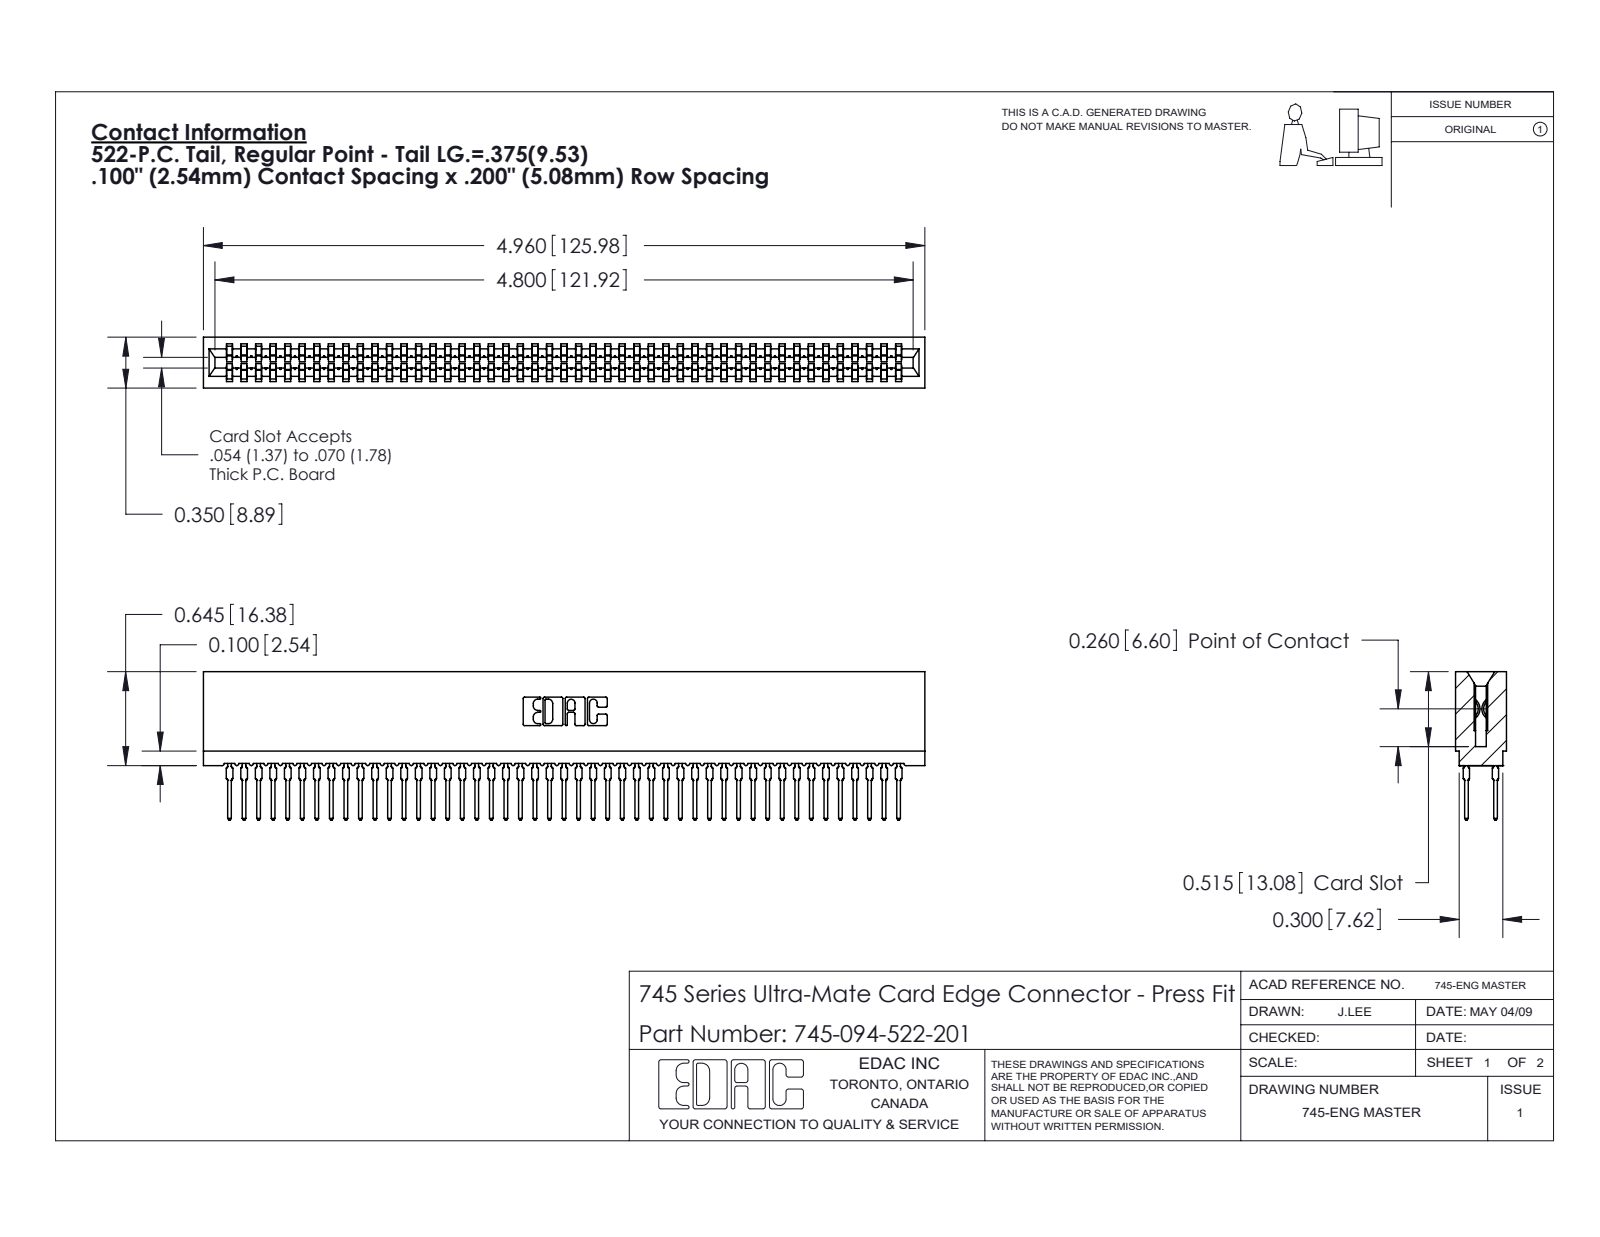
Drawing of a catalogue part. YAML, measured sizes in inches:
part_name: "745-292-001_522; 745-094-522-201; 745 Part_Insulator Option - 01"
step_written_by: "SolidWorks 2020 (CONFIG_CONTROL_DESIGN)"
units: inches
bodies: {solids: 95, faces: 8508, planar: 4379, cylindrical: 1685, other: 2444}
overall_size: [4.96, 1.021, 0.35]
volume: 0.697
surface_area: 36.65
partial_cylinders:
  - {radius: 0.021, count: 188}
  - {radius: 0.015, count: 94}
  - {radius: 0.01, count: 22}
  - {radius: 0.005, count: 8}
  - {radius: 0.011, count: 8}
  - {radius: 0.007, count: 6}
  - {radius: 0.031, count: 6}
  - {radius: 0.026, count: 3}
face_to_face_distances: [0.35, 0.063, 0.287, 0.2, 0.045, 0.305, 0.018, 0.243, 0.138, 0.212]
